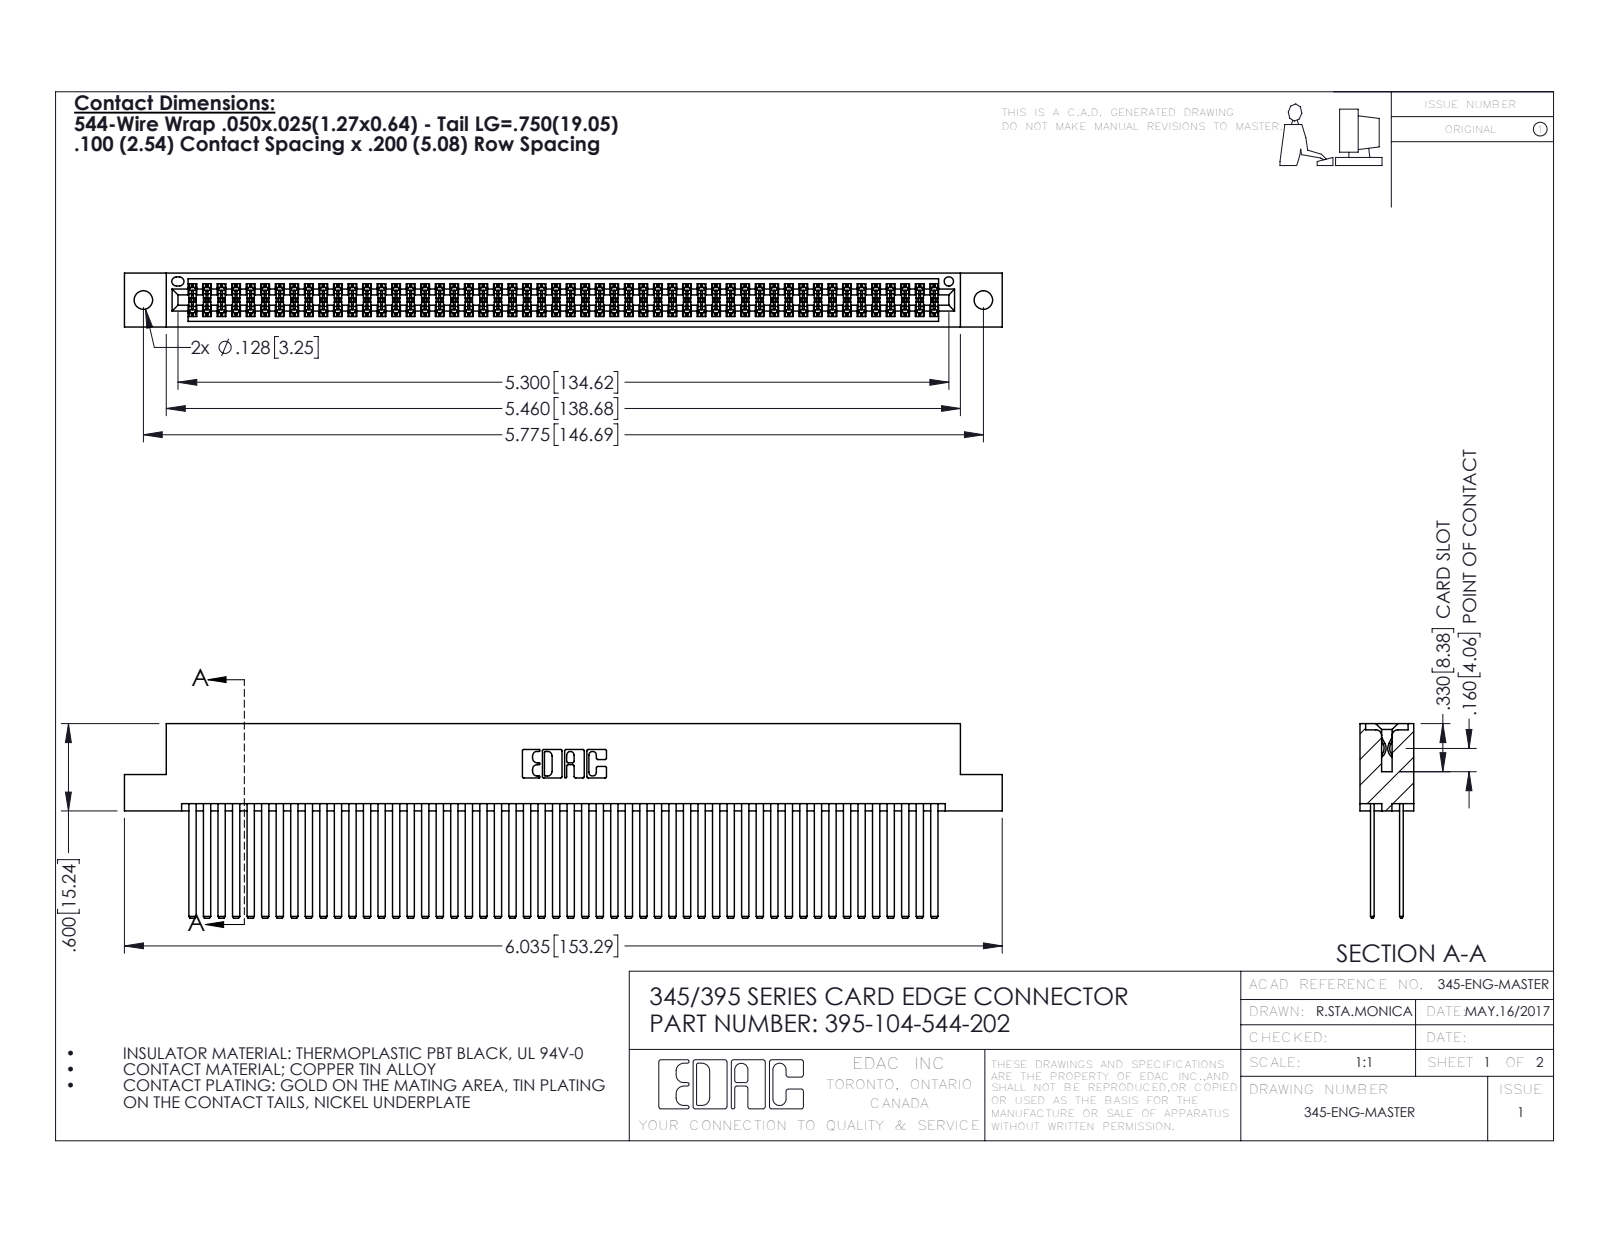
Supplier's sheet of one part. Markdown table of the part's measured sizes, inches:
| quantity | value |
| --- | --- |
| part name | 345-292-001_345-293-144; 345 Part_Flush Mounting Lugs - 0.128 Dia; 395-104-544-202 |
| STEP written by | SolidWorks 2016 (CONFIG_CONTROL_DESIGN) |
| units | inches |
| bodies | 105 solids, 4702 faces (3096 planar, 1606 cylindrical, 0 other) |
| overall size | 6.035 × 1.337 × 0.37 |
| volume | 1.001 in³ |
| surface area | 44.09 in² |
| round holes (diameter × count) | 0.128 × 2, 0.064 × 1 |
| partial cylindrical surfaces (radius × count) | 0.006 × 156, 0.01 × 22, 0.007 × 6, 0.031 × 6, 0.026 × 3, 0.014 × 2, 0.019 × 2, 0.022 × 2 |
| main face-to-face distances | 0.2, 0.025, 0.298, 0.072, 0.098, 0.272, 0.225, 0.175, 0.37, 0.05 |
| hole center spacings | 0.27, 5.539, 5.775 |
